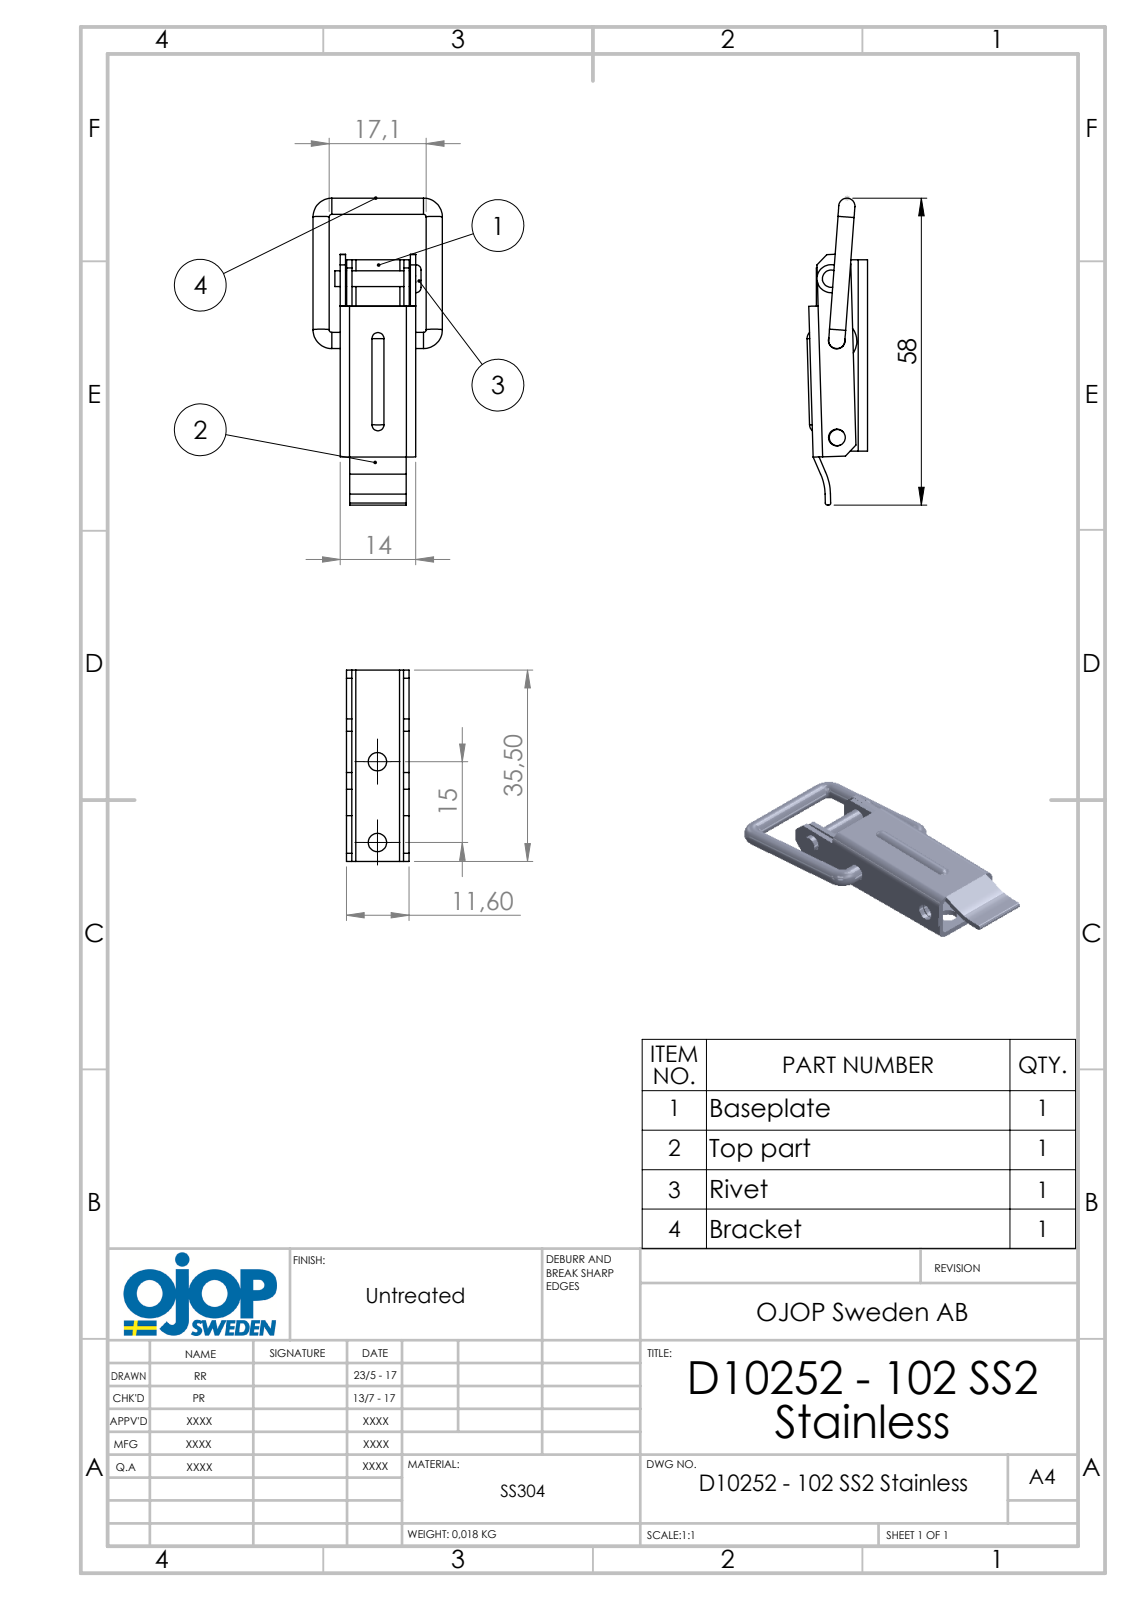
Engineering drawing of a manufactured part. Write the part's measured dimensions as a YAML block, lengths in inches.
part_name: "Underdel; Överdel; Nit; bygel (+1 more)"
step_written_by: "SolidWorks 2015 (AUTOMOTIVE_DESIGN)"
units: inches
bodies: {solids: 4, faces: 155, planar: 83, cylindrical: 57, other: 15}
overall_size: [2.361, 1.018, 0.442]
volume: 0.152
surface_area: 7.655
round_holes:
  - {diameter: 0.122, count: 3}
  - {diameter: 0.118, count: 2}
  - {diameter: 0.134, count: 2}
round_bosses_or_shafts:
  - {diameter: 0.118, count: 4}
  - {diameter: 0.114, count: 1}
partial_cylinders:
  - {radius: 0.029, count: 4}
  - {radius: 0.069, count: 4}
  - {radius: 0.016, count: 2}
  - {radius: 0.02, count: 1}
  - {radius: 0.059, count: 1}
  - {radius: 0.156, count: 1}
  - {radius: 0.276, count: 1}
  - {radius: 0.394, count: 1}
face_to_face_distances: [0.039, 0.512, 0.413, 0.465, 0.047, 0.051, 0.461, 0.551, 0.472, 0.374]
hole_center_spacings: [0.473, 0.591, 0.709, 0.71, 1.181, 1.182]
